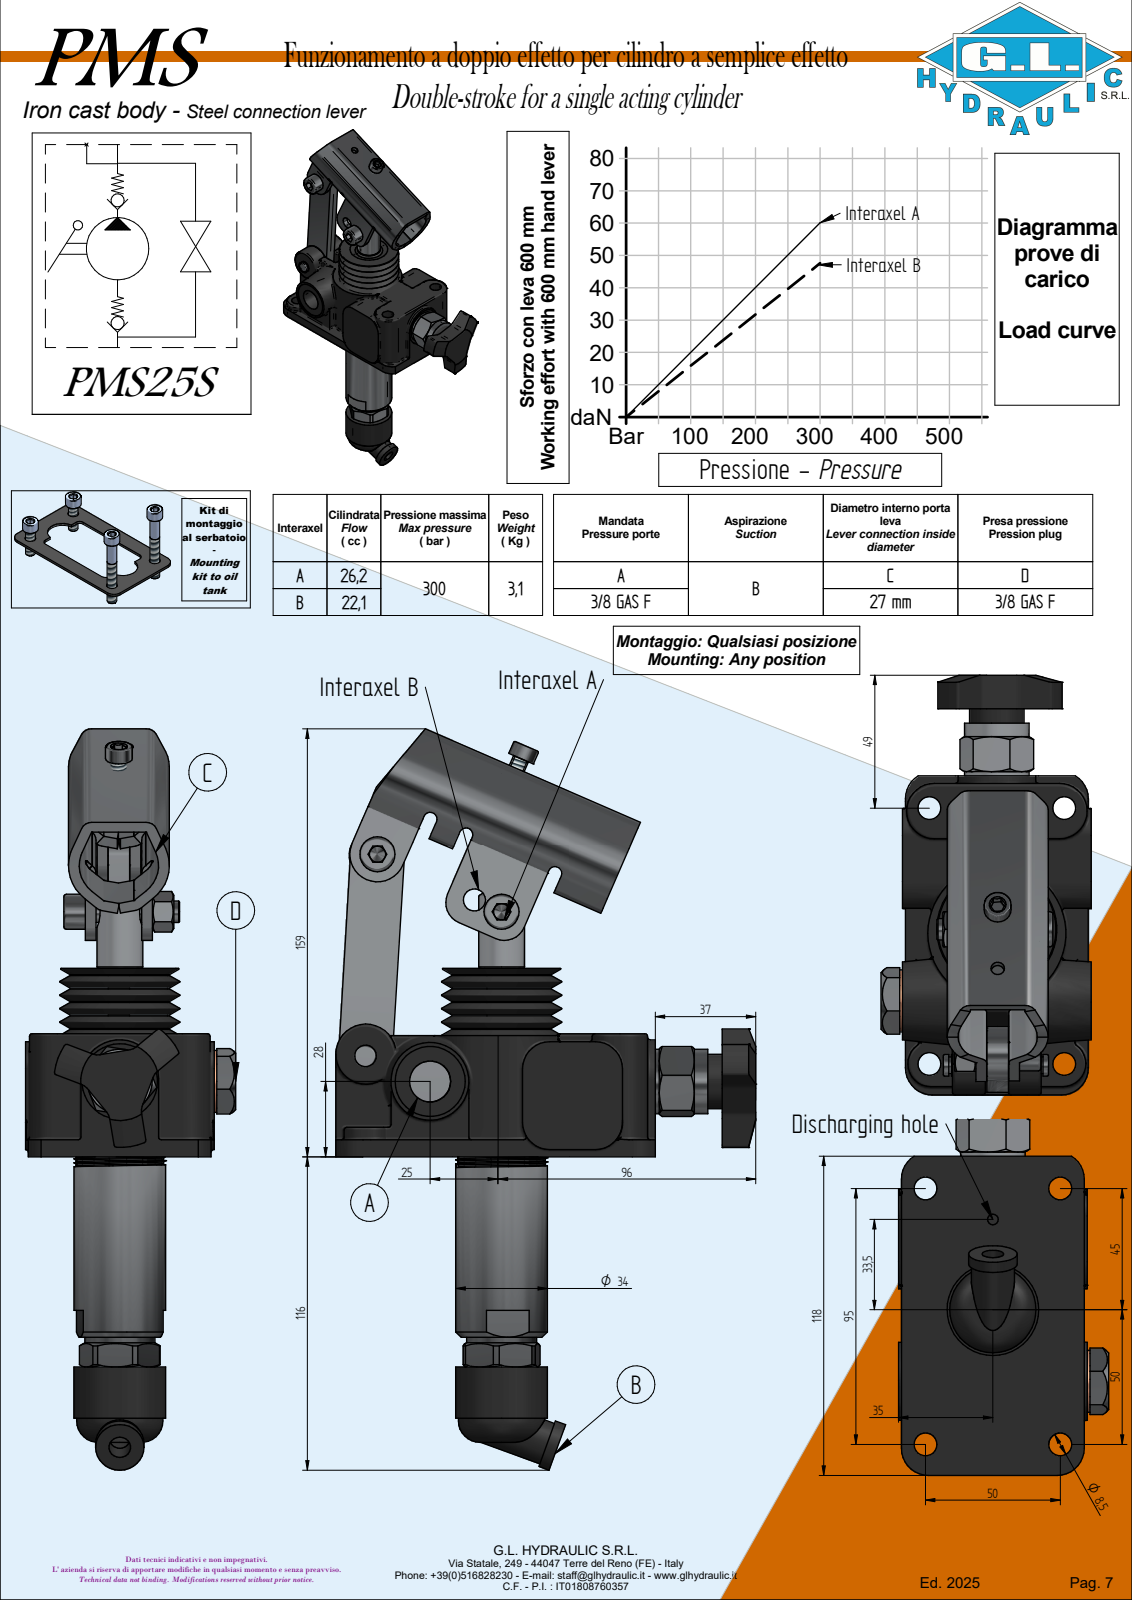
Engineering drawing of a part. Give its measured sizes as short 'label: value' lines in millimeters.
name: PM25S
written by: Solid Edge (AUTOMOTIVE_DESIGN)
unit: mm
bodies: 2 solids, 46 faces (32 planar, 5 cylindrical, 9 other)
size: 138.35 × 52.62 × 48.32
volume: 7 021 mm³; area: 2 855 mm²
holes: 1× ⌀17
bosses: 1× ⌀23, 1× ⌀17.3, 1× ⌀10, 1× ⌀6
face distances: 21.99, 8.5, 12.5, 21, 5, 1.5, 14, 7, 3.5, 12
